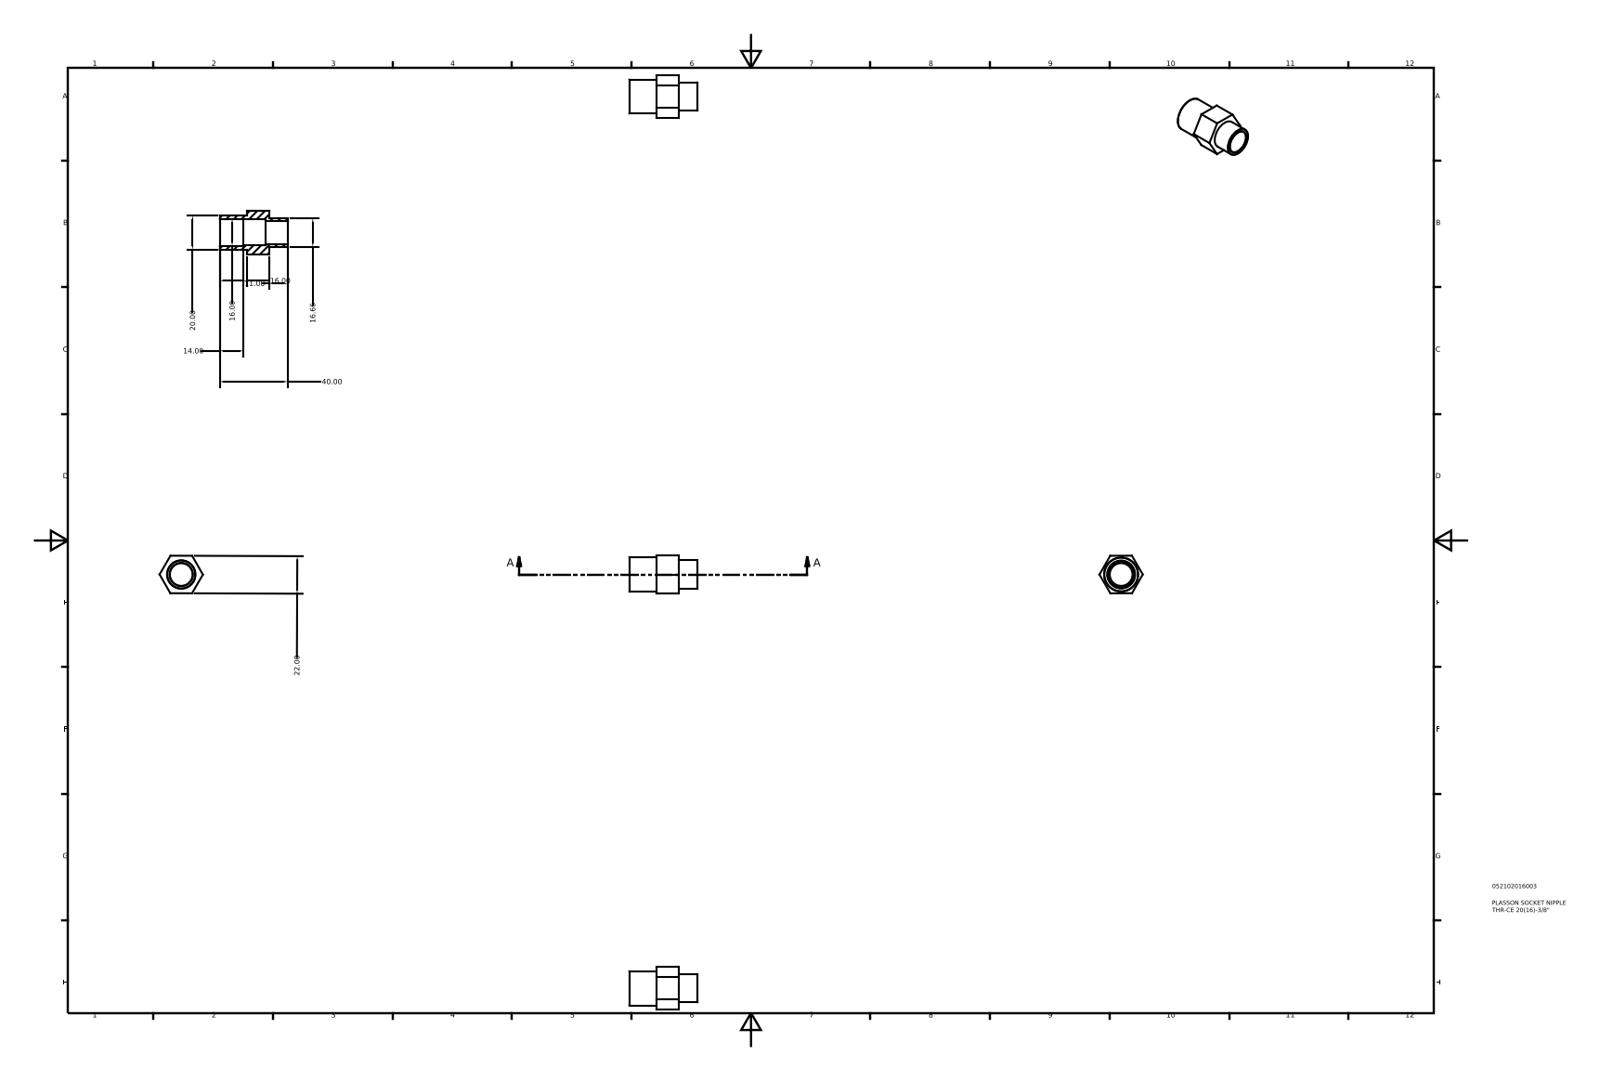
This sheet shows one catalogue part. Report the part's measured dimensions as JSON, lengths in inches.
{"part_name": "052102016003", "step_written_by": "Autodesk Inventor 2015 (AUTOMOTIVE_DESIGN)", "units": "inches", "bodies": {"solids": 1, "faces": 21, "planar": 12, "cylindrical": 5, "other": 4}, "overall_size": [1.575, 1, 0.868], "volume_in3": 0.36, "surface_area_in2": 7.727, "round_holes": [[0.525, 1], [0.598, 1], [0.63, 1]], "round_bosses_or_shafts": [[0.787, 1], [0.656, 1]], "face_to_face_distances": [0.866, 0.512, 0.63, 1.142, 1.575, 0.945, 0.433, 1.055, 0.425, 0.087]}
